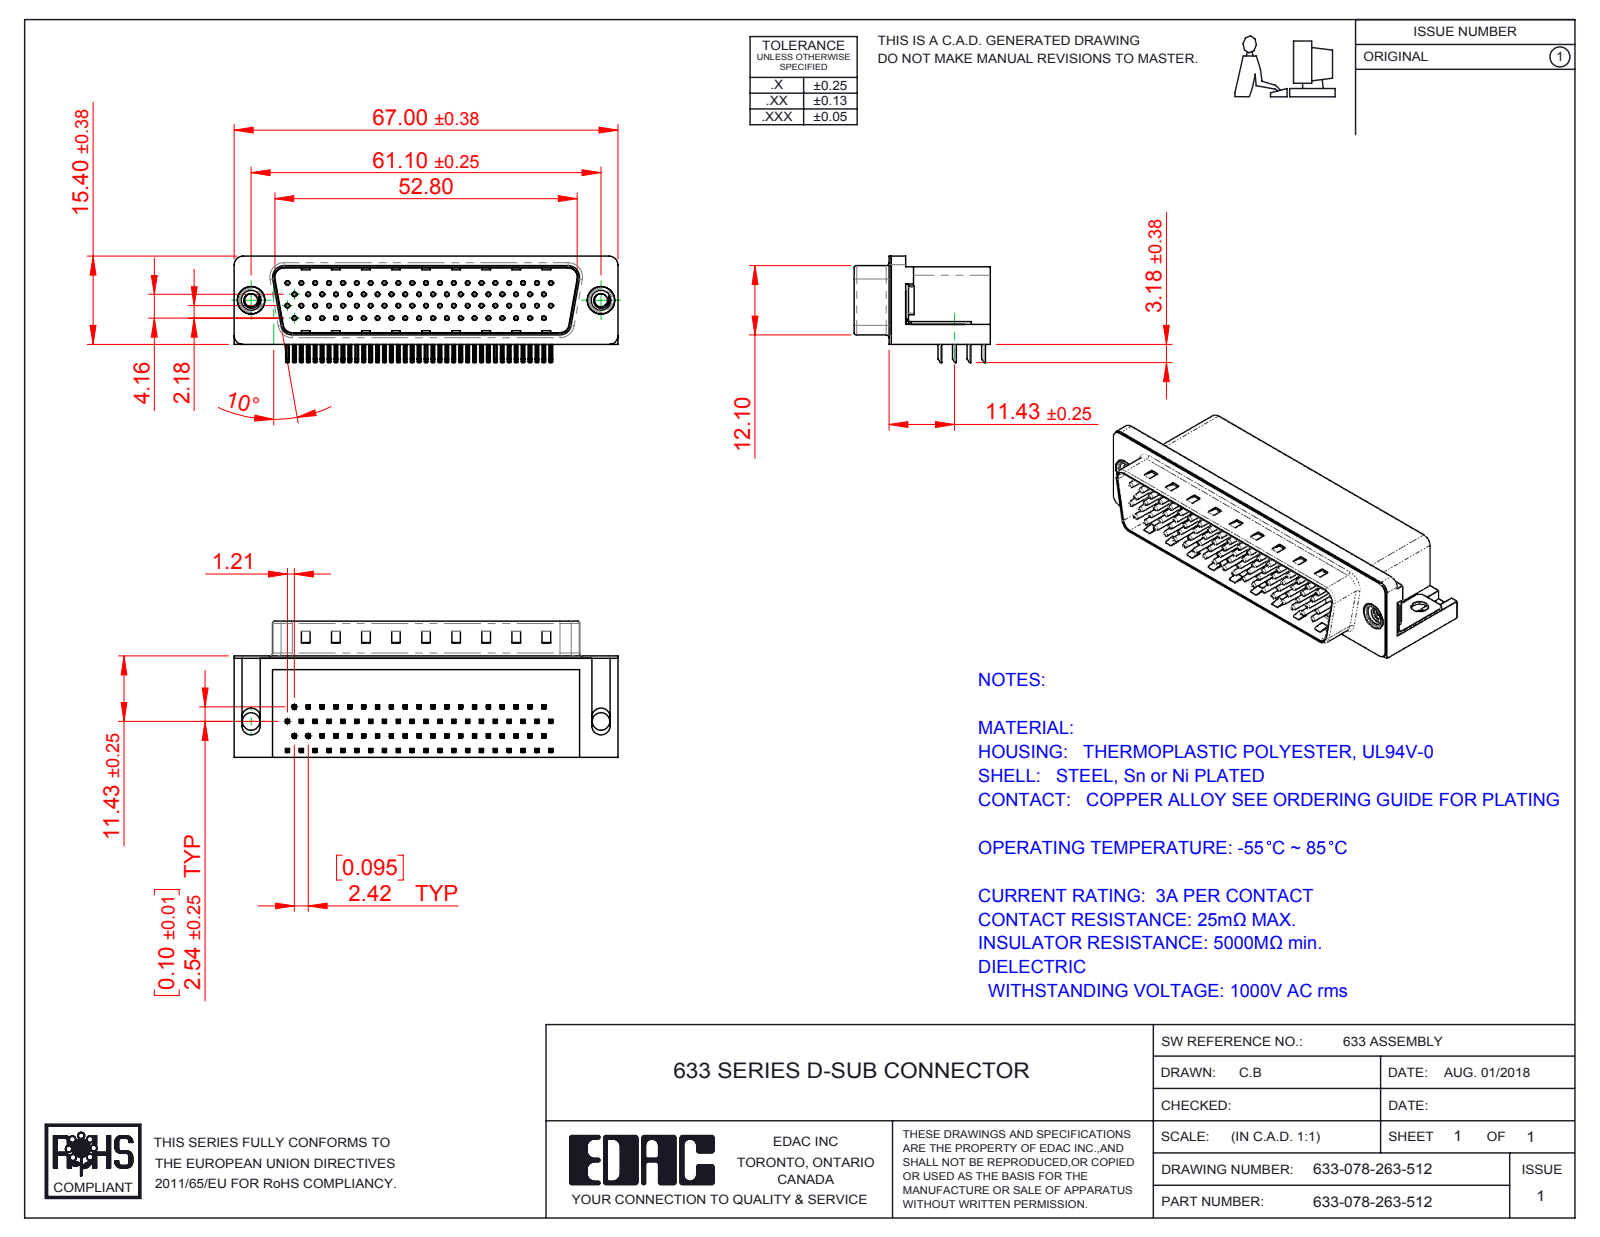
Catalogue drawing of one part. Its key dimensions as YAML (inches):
part_name: "633 Contact Bottom_78 Contact; 633 Contact Middle_78 Contact; 633 Contact Top_78 Contact; 633 Contact Top 78 (+5 more)"
step_written_by: "SolidWorks 2016 (CONFIG_CONTROL_DESIGN)"
units: inches
bodies: {solids: 84, faces: 6274, planar: 3979, cylindrical: 1778, other: 517}
overall_size: [2.638, 0.937, 0.731]
volume: 0.892
surface_area: 25.32
round_holes:
  - {diameter: 0.014, count: 78}
  - {diameter: 0.031, count: 78}
  - {diameter: 0.089, count: 2}
  - {diameter: 0.12, count: 2}
  - {diameter: 0.157, count: 2}
  - {diameter: 0.189, count: 2}
  - {diameter: 0.197, count: 2}
round_bosses_or_shafts:
  - {diameter: 0.03, count: 78}
  - {diameter: 0.193, count: 2}
  - {diameter: 0.187, count: 2}
  - {diameter: 0.154, count: 2}
partial_cylinders:
  - {radius: 0.01, count: 320}
  - {radius: 0.005, count: 156}
  - {radius: 0.039, count: 16}
  - {radius: 0.02, count: 9}
  - {radius: 0.063, count: 8}
  - {radius: 0.059, count: 6}
  - {radius: 0.018, count: 4}
  - {radius: 0.035, count: 4}
face_to_face_distances: [0.016, 0.52, 0.681, 0.461, 0.526, 0.081, 0.541, 0.065, 0.073, 0.469]
hole_center_spacings: [0.095, 0.191, 0.286, 0.381, 0.246, 0.281, 0.476, 0.339]
